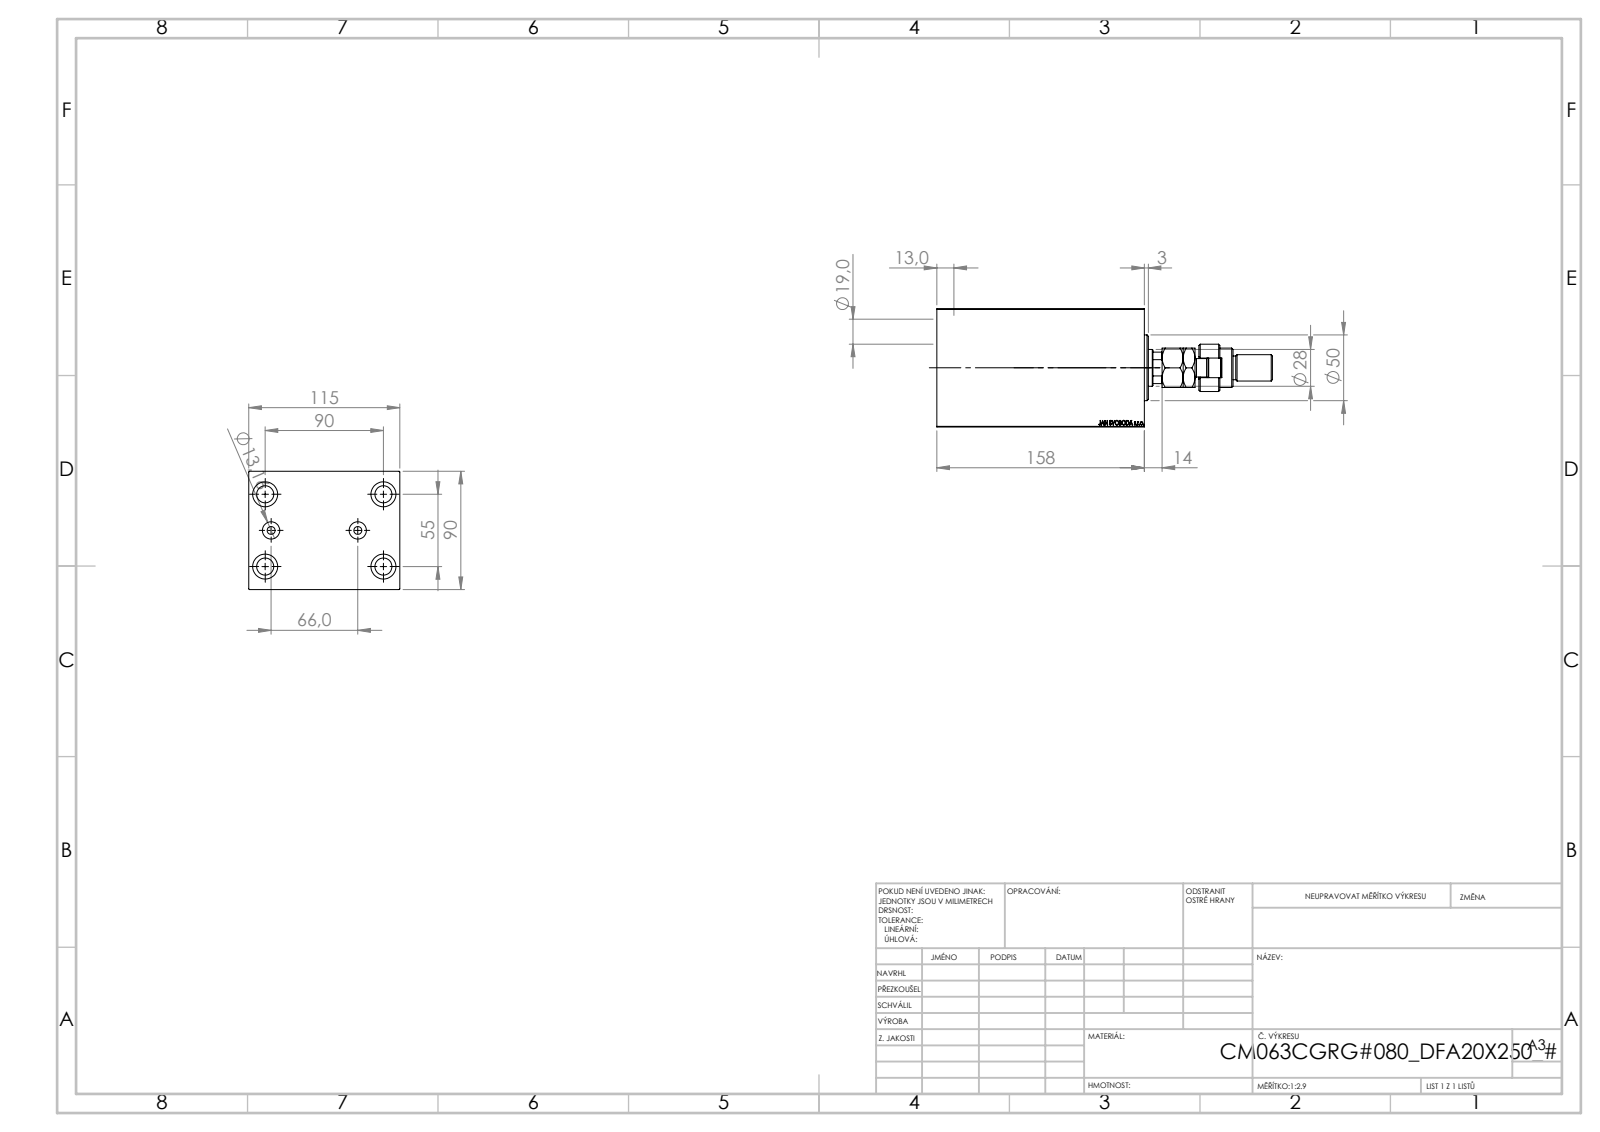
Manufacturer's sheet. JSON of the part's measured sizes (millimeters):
{"part_name": "V450CM_VC_B; V450CM_C_Body; MFA; FEMALE_PART_FOR_DFA (+1 more)", "step_written_by": "SolidWorks 2019 (CONFIG_CONTROL_DESIGN)", "units": "millimeters", "bodies": {"solids": 5, "faces": 946, "planar": 437, "cylindrical": 71, "other": 438}, "overall_size": [255.5, 115, 90], "volume_mm3": 1379000, "surface_area_mm2": 197189, "round_holes": [[13, 4], [19, 4], [6, 2], [13.16, 2], [18.5, 1], [28, 1], [31.5, 1], [63, 1], [65, 1], [72, 1]], "round_bosses_or_shafts": [[50, 1], [36, 1], [30, 1], [22, 1], [20, 1], [18, 1], [14, 1]], "partial_cylinders_radius": [[7.5, 1], [12, 1], [13.5, 1]], "face_to_face_distances": [90, 115, 158, 17.5, 140.5, 29.3, 111.2, 128.7, 80, 109.3], "hole_center_spacings": [30, 52.74, 82.71, 33, 55, 90, 105.48, 66]}
